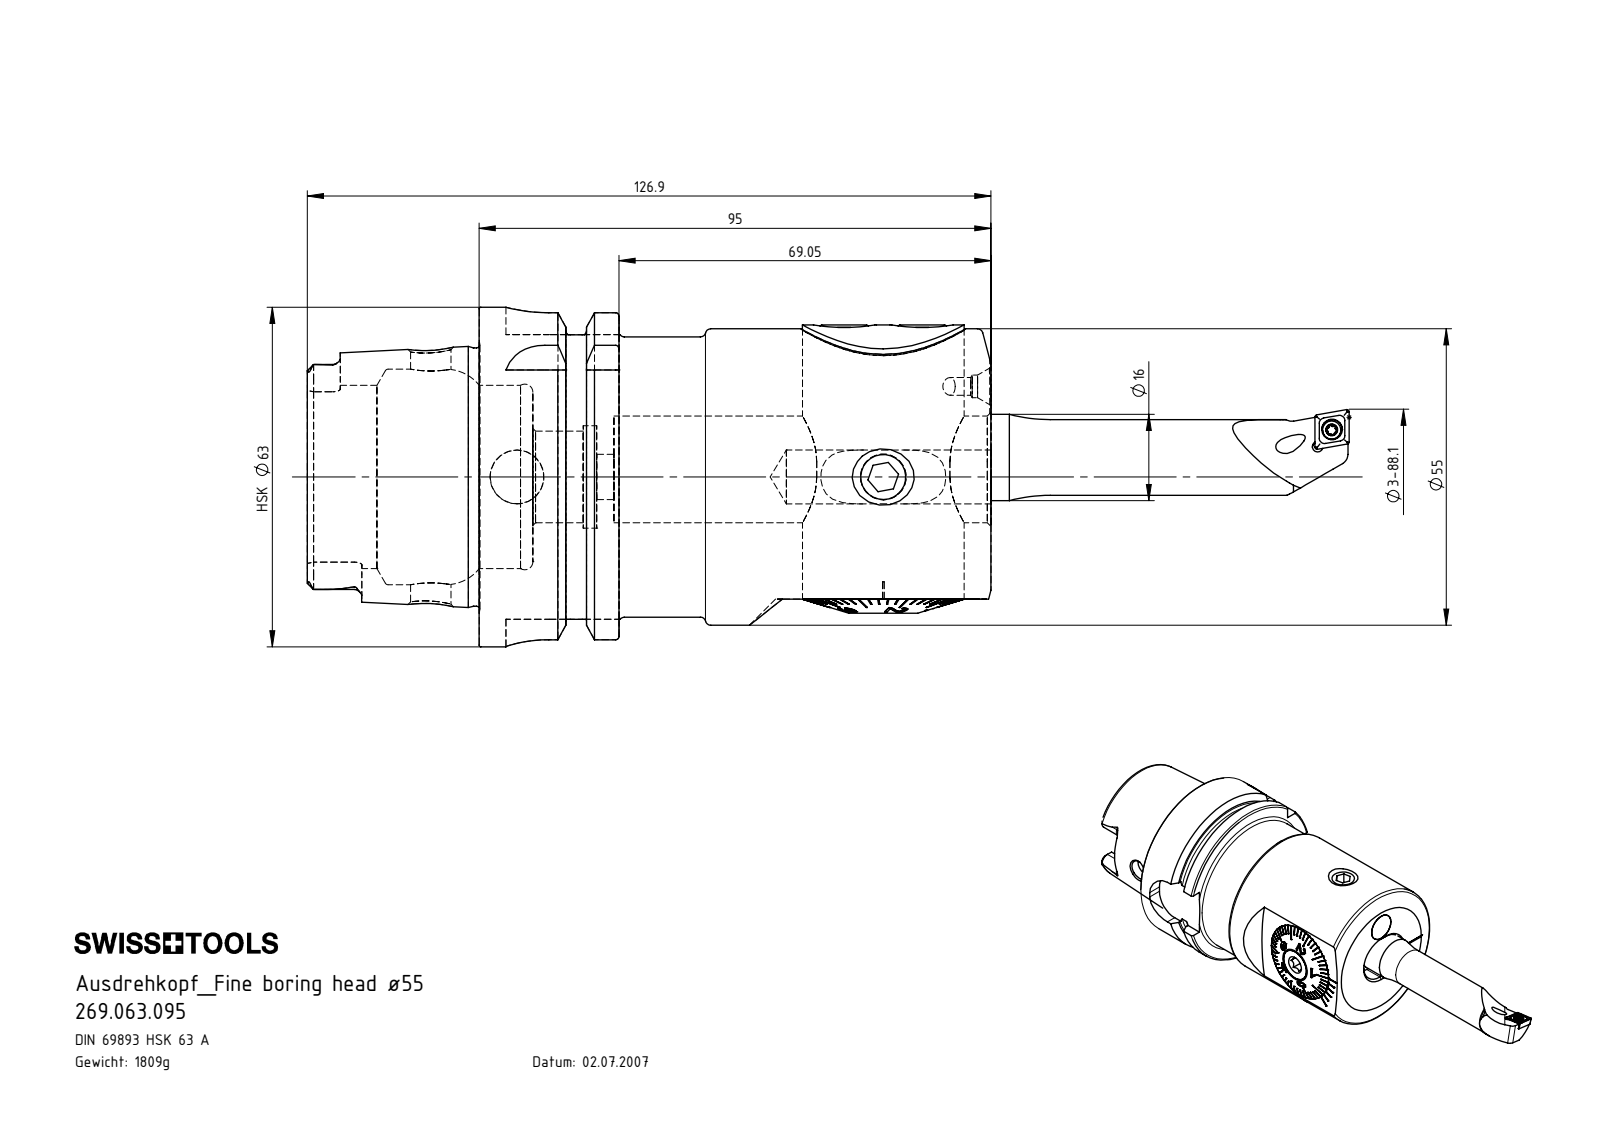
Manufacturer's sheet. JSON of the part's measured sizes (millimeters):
{"part_name": "A55-BG2.012.006_B; WCB-ER2.001.009_A; A55-BG1.011.041; Klebstoff D10 (+8 more)", "step_written_by": "SolidWorks 2017 (CONFIG_CONTROL_DESIGN)", "units": "millimeters", "bodies": {"solids": 17, "faces": 947, "planar": 374, "cylindrical": 201, "other": 372}, "overall_size": [193.39, 63, 63], "volume_mm3": 230685, "surface_area_mm2": 62302, "round_holes": [[8.5, 3], [2, 2], [3, 2], [10, 2], [1, 1], [1.6, 1], [2.05, 1], [2.8, 1], [3.3, 1], [3.85, 1], [4.2, 1], [7.5, 1]], "round_bosses_or_shafts": [[10, 3], [63, 1], [55, 1], [54.95, 1], [52, 1], [47.93, 1], [30, 1], [29.98, 1]], "partial_cylinders_radius": [[0.21, 6], [0.34, 6], [0.59, 6], [1.4, 6], [0.36, 5], [2.88, 4], [8, 4], [3.2, 3]], "face_to_face_distances": [95, 6.8, 16, 25.95, 69.05, 4, 2.8, 2.5, 9.95, 85.05], "hole_center_spacings": [7.25, 14.5, 3.63, 4.05, 4.15, 14.95, 15.67, 18.83]}
